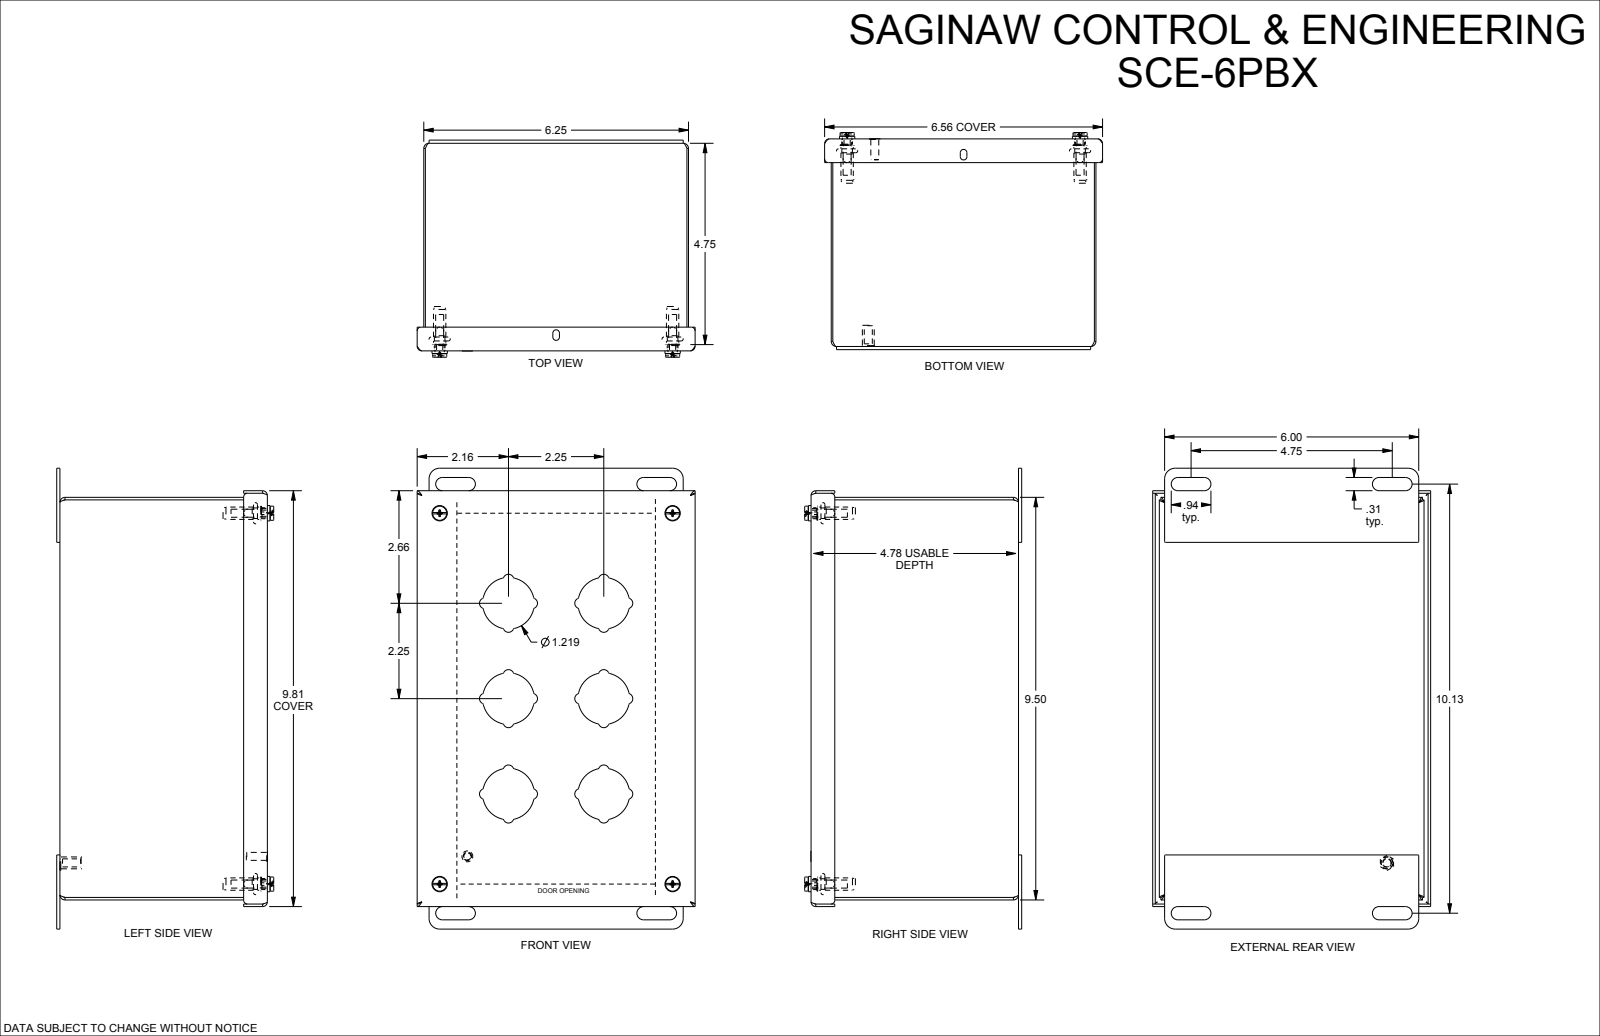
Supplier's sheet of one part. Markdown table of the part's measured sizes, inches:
| quantity | value |
| --- | --- |
| part name | SCE-6PBX-RAL1018 |
| STEP written by | SolidWorks 2021 (AUTOMOTIVE_DESIGN) |
| units | inches |
| bodies | 19 solids, 603 faces (205 planar, 236 cylindrical, 162 other) |
| overall size | 10.875 × 6.56 × 5.124 |
| volume | 19.91 in³ |
| surface area | 660 in² |
| round holes (diameter × count) | 0.19 × 5, 0.22 × 4, 0.25 × 4, 0.25 × 4, 0.317 × 4 |
| round bosses / shafts (diameter × count) | 0.188 × 5, 0.437 × 4, 0.362 × 4, 0.34 × 4, 0.334 × 4, 0.292 × 4, 0.27 × 4, 0.26 × 4 |
| partial cylindrical surfaces (radius × count) | 0.04 × 48, 0.125 × 24, 0.06 × 12, 0.015 × 8, 0.115 × 8, 0.156 × 8, 0.245 × 8, 0.609 × 6 |
| main face-to-face distances | 0.06, 4.838, 6.19, 4.778, 9.44, 4.898, 6.25, 6.13, 9.5, 9.38 |
| hole center spacings | 8.75, 5.5, 8.75, 10.335, 5.497, 5.5, 8.747, 10.335 |
